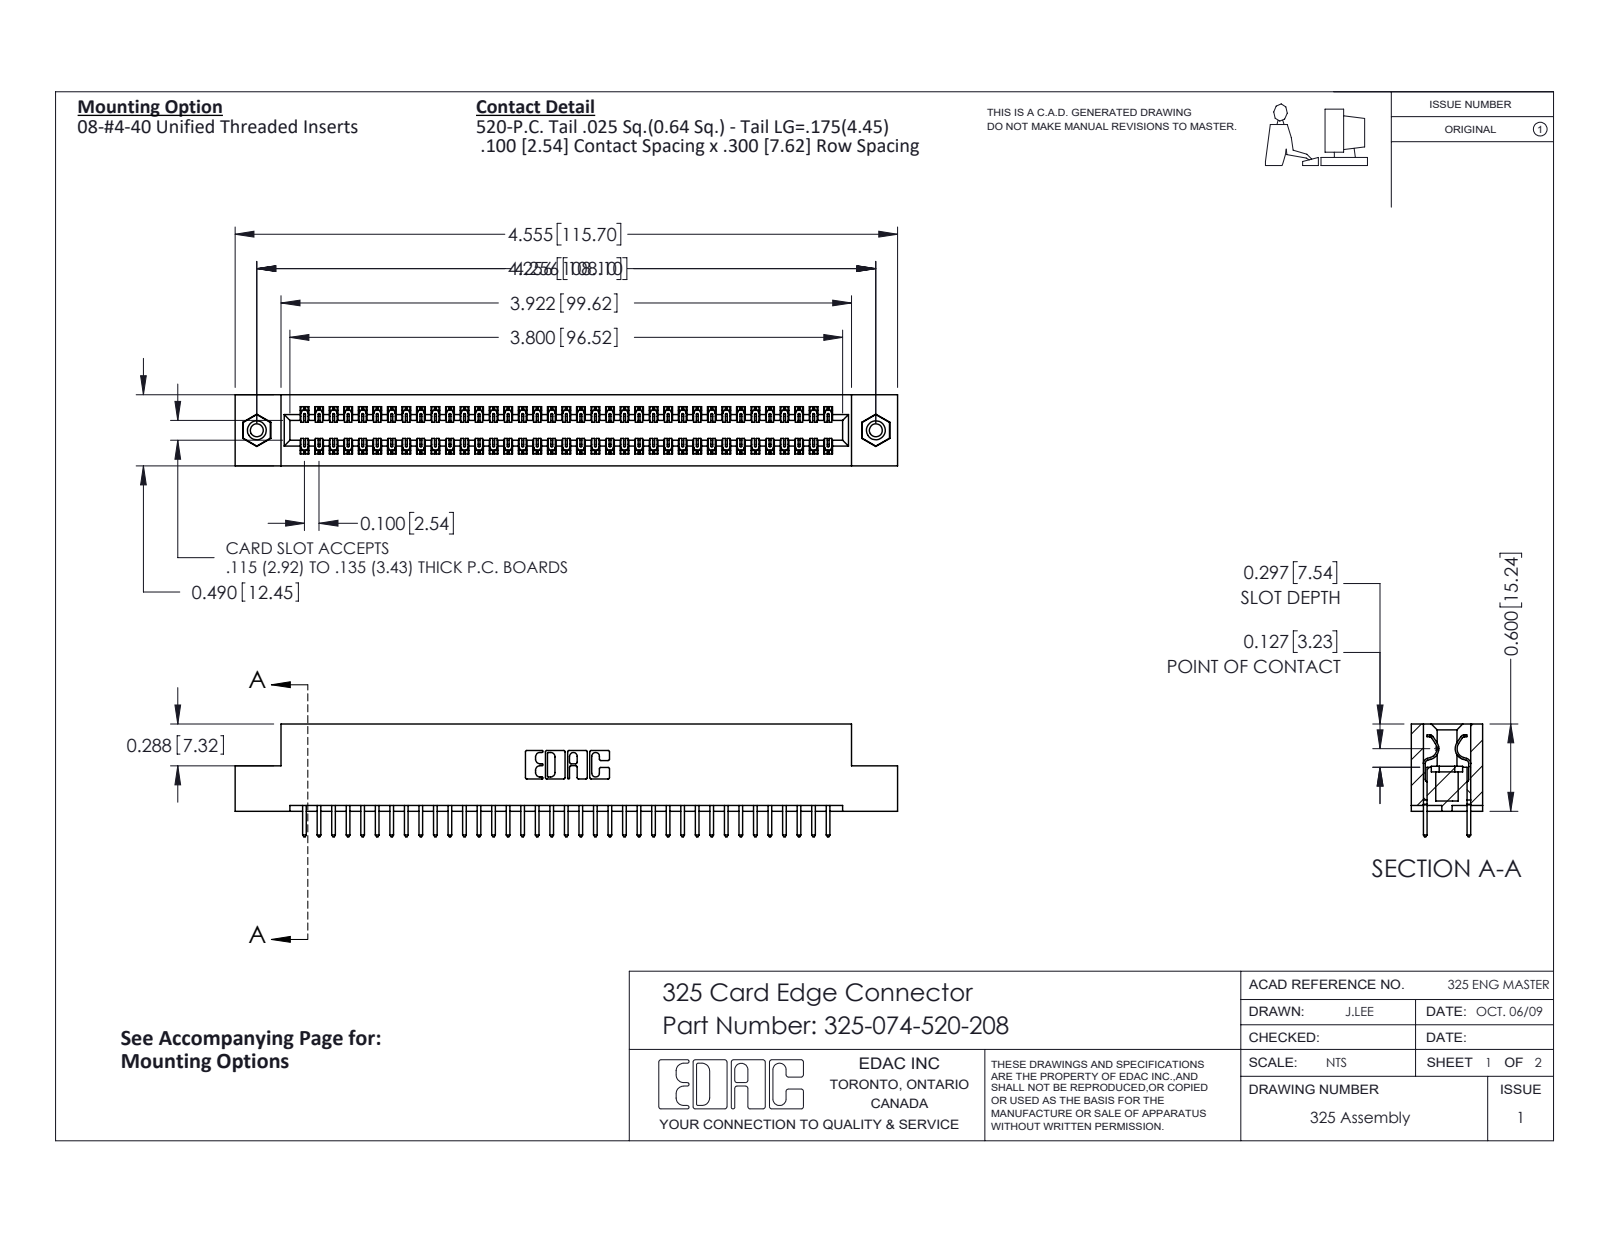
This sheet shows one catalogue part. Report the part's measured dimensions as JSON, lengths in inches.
{"part_name": "345-250-001_345-250-003-102; 325-292-001_325-293-120; 325-074-520-208; 325 Part_TI", "step_written_by": "SolidWorks 2016 (CONFIG_CONTROL_DESIGN)", "units": "inches", "bodies": {"solids": 77, "faces": 4022, "planar": 2766, "cylindrical": 1240, "other": 16}, "overall_size": [4.555, 0.775, 0.49], "volume_in3": 0.908, "surface_area_in2": 27.51, "round_holes": [[0.089, 2], [0.125, 2], [0.16, 2]], "round_bosses_or_shafts": [[0.155, 2]], "partial_cylinders_radius": [[0.006, 111], [0.01, 74], [0.01, 22], [0.007, 6], [0.031, 6], [0.026, 3], [0.014, 2], [0.022, 2]], "face_to_face_distances": [0.083, 0.407, 0.49, 0.3, 0.107, 0.383, 0.025, 0.325, 0.275, 0.56], "hole_center_spacings": [4.256]}
